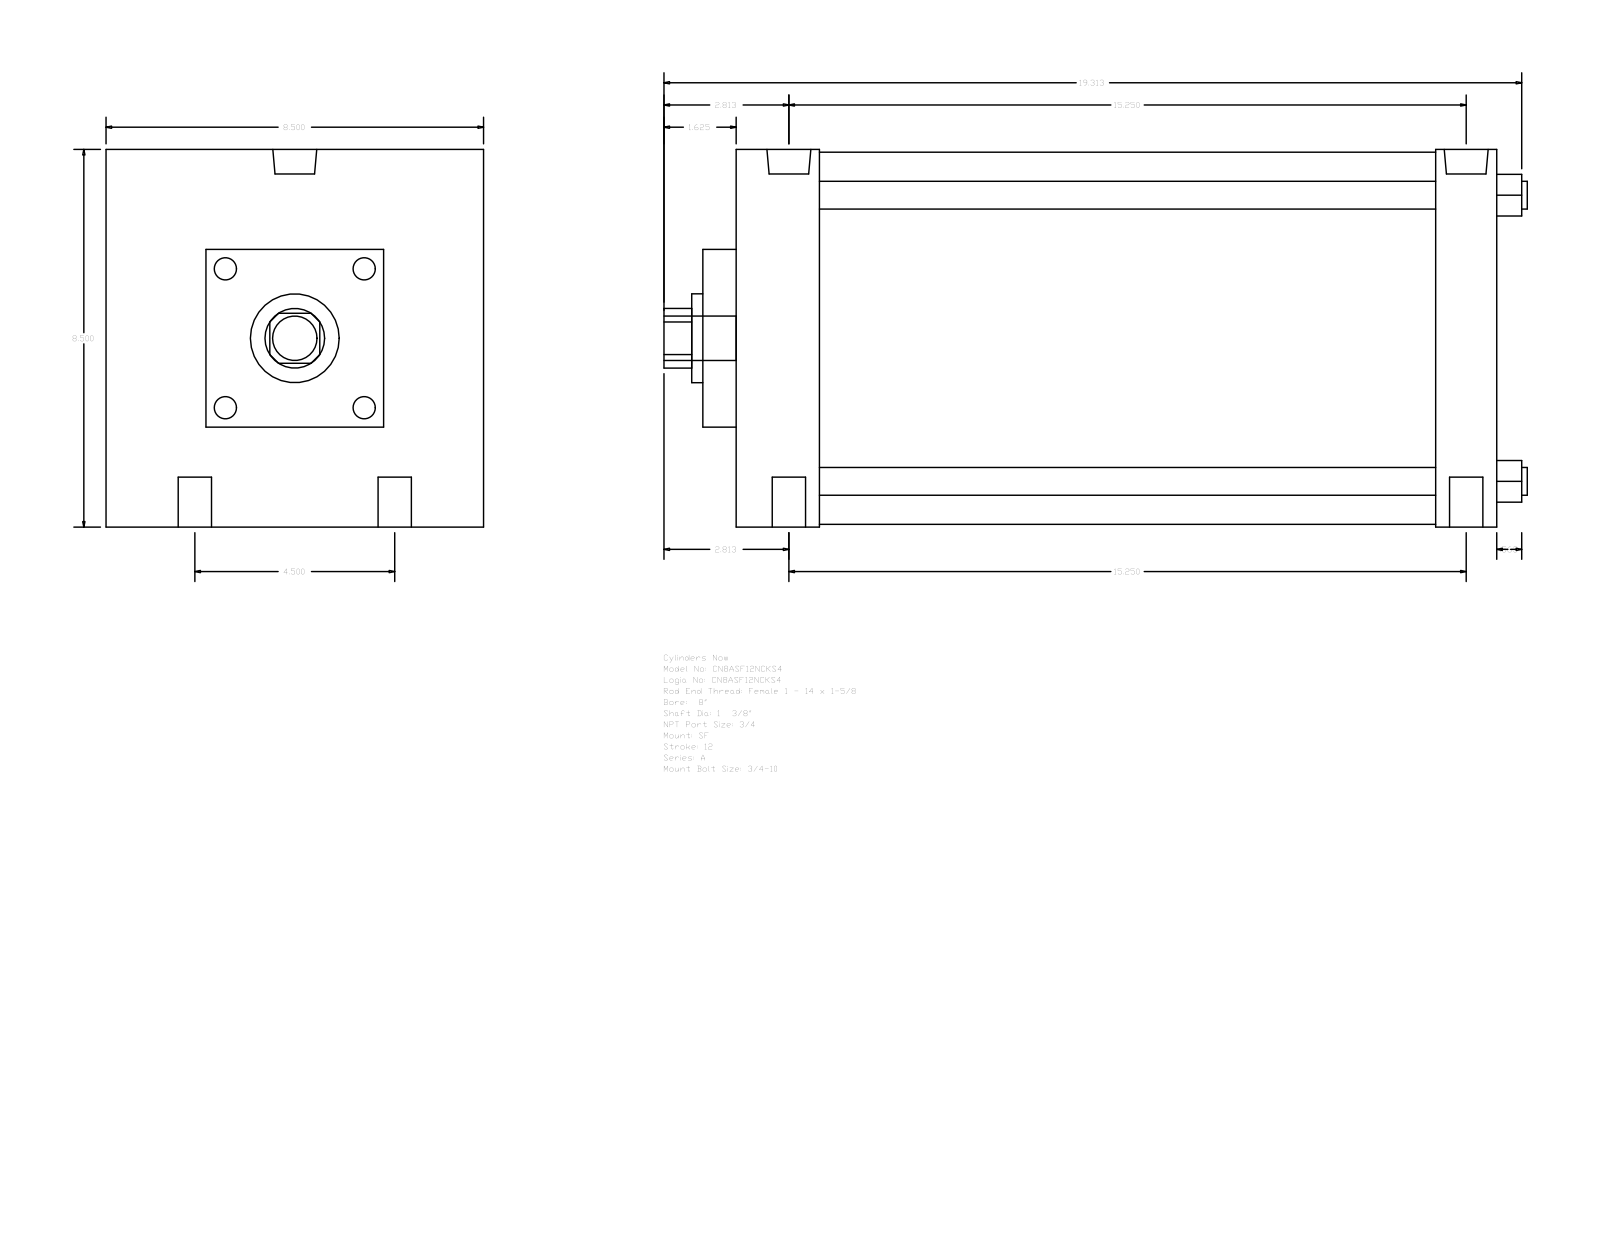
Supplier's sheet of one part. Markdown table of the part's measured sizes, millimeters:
| quantity | value |
| --- | --- |
| part name | A_SF__0800_1.375 |
| STEP written by | GSSL Pune (CONFIG_CONTROL_DESIGN) |
| units | millimeters |
| bodies | 0 solids, 93 faces (67 planar, 26 cylindrical, 0 other) |
| overall size | 493.71 × 215.9 × 215.9 |
| round holes (diameter × count) | 19.05 × 4, 15.08 × 2, 25.12 × 2, 34.92 × 1, 50.8 × 1 |
| round bosses / shafts (diameter × count) | 15.88 × 4, 212.72 × 1, 25.4 × 1 |
| partial cylindrical surfaces (radius × count) | 17.06 × 1 |
| main face-to-face distances | 434.98, 215.9, 47.63, 400.05, 352.42, 387.35, 34.93, 19.04, 66.67, 419.09 |
| hole center spacings | 57.15, 391.54, 387.35, 114.3, 403.86, 374.65 |
